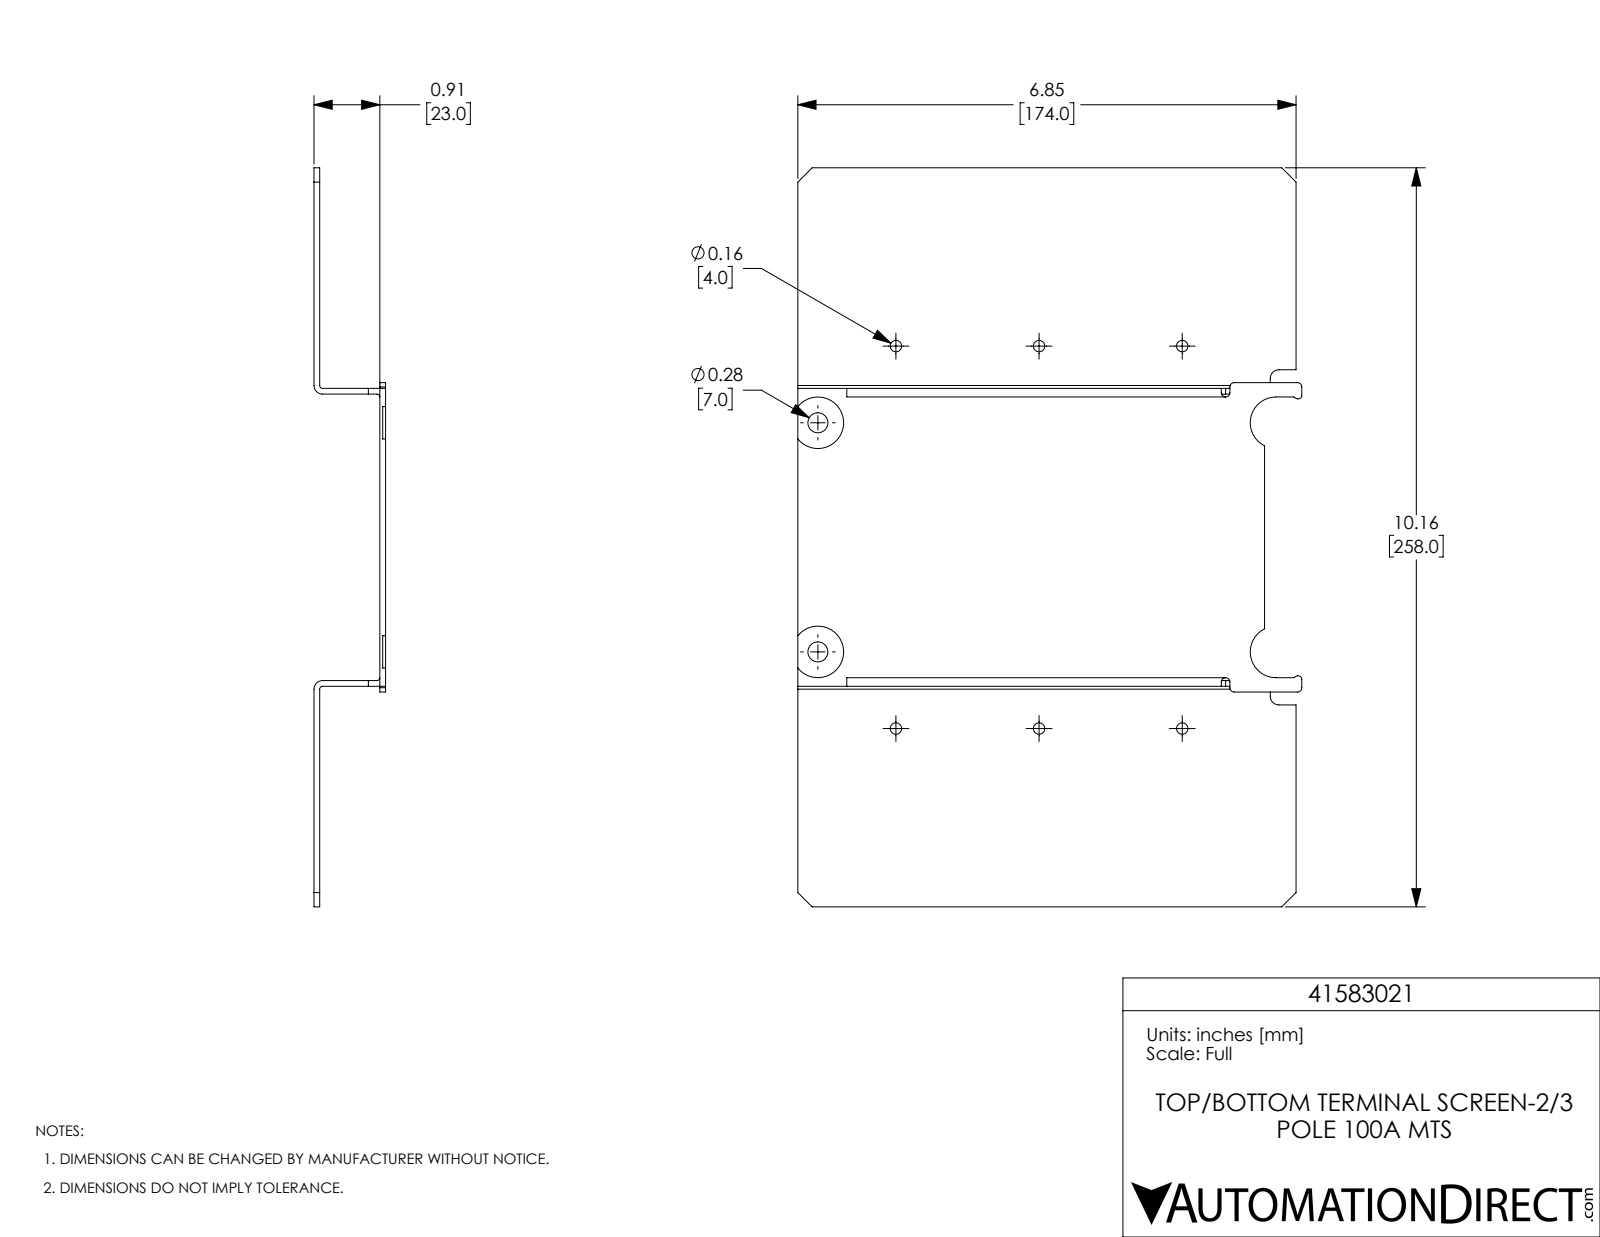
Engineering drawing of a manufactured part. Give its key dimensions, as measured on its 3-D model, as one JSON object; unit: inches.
{"part_name": "41583021", "step_written_by": "SolidWorks 2017 (AUTOMOTIVE_DESIGN)", "units": "inches", "bodies": {"solids": 1, "faces": 97, "planar": 44, "cylindrical": 53, "other": 0}, "overall_size": [10.157, 6.929, 0.984], "volume_in3": 6.11, "surface_area_in2": 159.8, "round_holes": [[0.157, 6], [0.276, 2]], "partial_cylinders_radius": [[0.059, 7], [0.118, 6], [0.039, 4], [0.354, 4], [0.049, 2], [0.12, 2], [0.079, 1]], "face_to_face_distances": [0.079, 0.906, 0.827, 0.984, 4.016, 4.094, 3.937, 0.039, 3.031, 3.11], "hole_center_spacings": [1.969, 5.613, 5.256, 1.504, 3.219, 3.937, 4.337, 5.119]}
